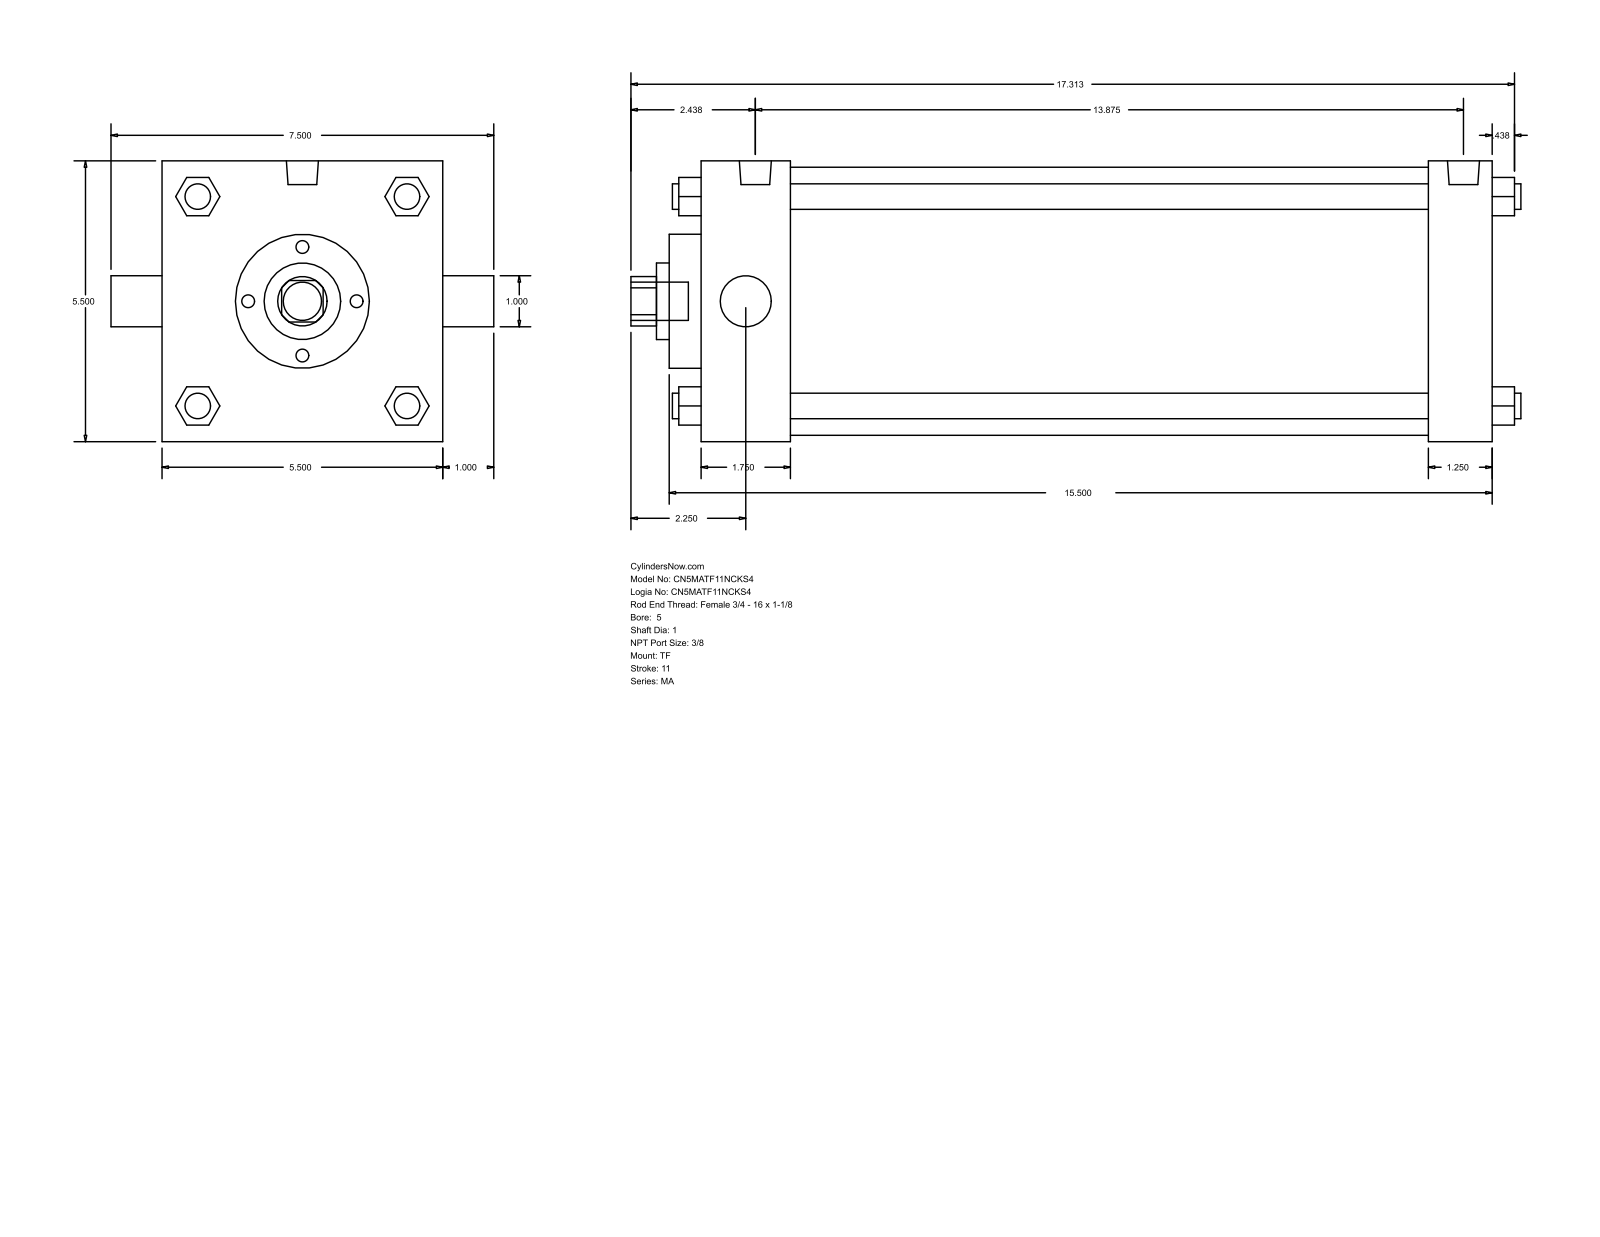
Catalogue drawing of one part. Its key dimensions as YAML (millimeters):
part_name: "MA_TF__0500_1"
step_written_by: "GSSL Pune (CONFIG_CONTROL_DESIGN)"
units: millimeters
bodies: {solids: 0, faces: 122, planar: 93, cylindrical: 29, other: 0}
overall_size: [442.91, 190.5, 139.7]
round_holes:
  - {diameter: 25.4, count: 2}
  - {diameter: 38.1, count: 1}
  - {diameter: 66.67, count: 1}
  - {diameter: 133.35, count: 1}
round_bosses_or_shafts:
  - {diameter: 12.7, count: 4}
  - {diameter: 11.11, count: 3}
  - {diameter: 15.93, count: 2}
  - {diameter: 19.05, count: 1}
partial_cylinders:
  - {radius: 12.29, count: 1}
face_to_face_distances: [139.7, 393.7, 361.96, 31.74, 44.46, 317.5, 349.24, 15.87, 60.33, 377.83]
